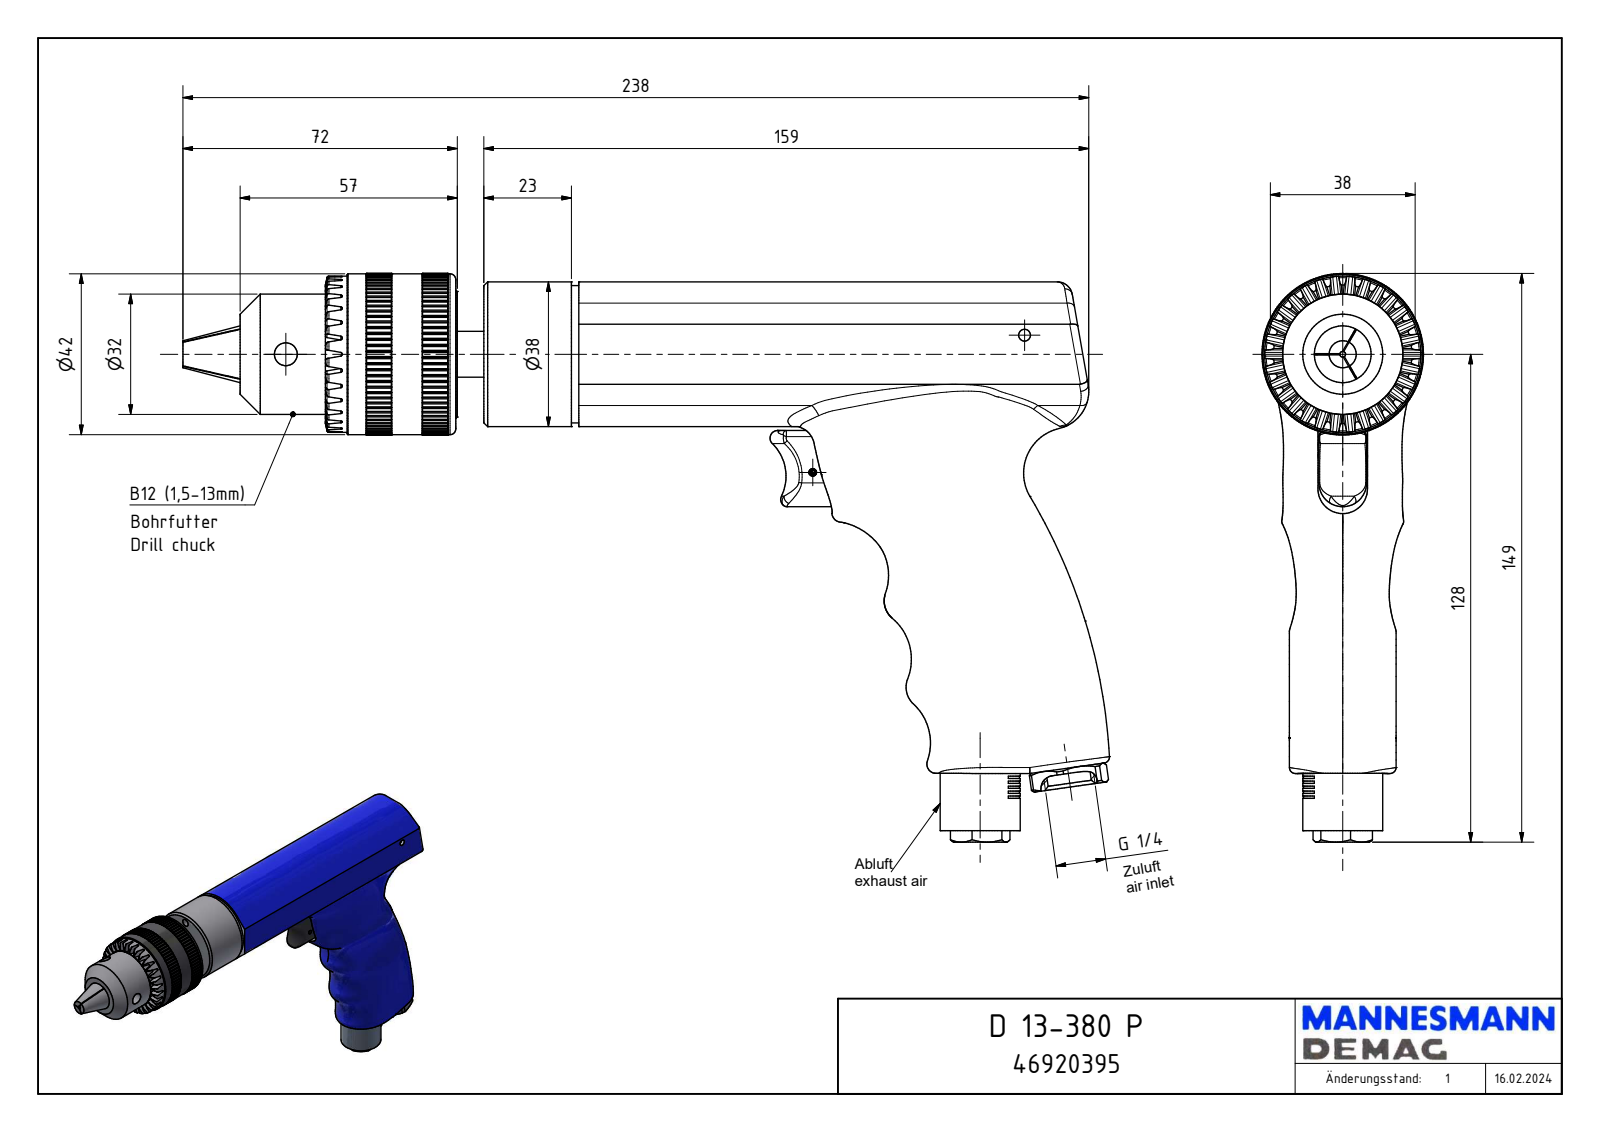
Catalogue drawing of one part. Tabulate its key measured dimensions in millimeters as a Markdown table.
| quantity | value |
| --- | --- |
| part name | D 13-380 P_46920395 |
| STEP written by | Autodesk Inventor 2008 (AUTOMOTIVE_DESIGN) |
| units | millimeters |
| bodies | 1 solid, 1773 faces (742 planar, 387 cylindrical, 644 other) |
| overall size | 243.18 × 149.2 × 42.4 |
| volume | 361 689 mm³ |
| surface area | 55 903 mm² |
| round holes (diameter × count) | 1.5 × 1, 3.1 × 1, 6.4 × 1, 11.09 × 1, 12.5 × 1, 17 × 1, 24 × 1, 36.2 × 1 |
| round bosses / shafts (diameter × count) | 42.2 × 1, 41 × 1, 38 × 1, 36 × 1, 33.57 × 1, 31.55 × 1, 21 × 1, 16.66 × 1 |
| partial cylindrical surfaces (radius × count) | 0.5 × 75, 1.6 × 18, 2 × 6, 10 × 4, 4 × 3, 6.5 × 2, 0.34 × 1, 0.45 × 1 |
| main face-to-face distances | 38, 5, 9, 29, 14, 15, 7.22, 24, 12.5, 20 |
